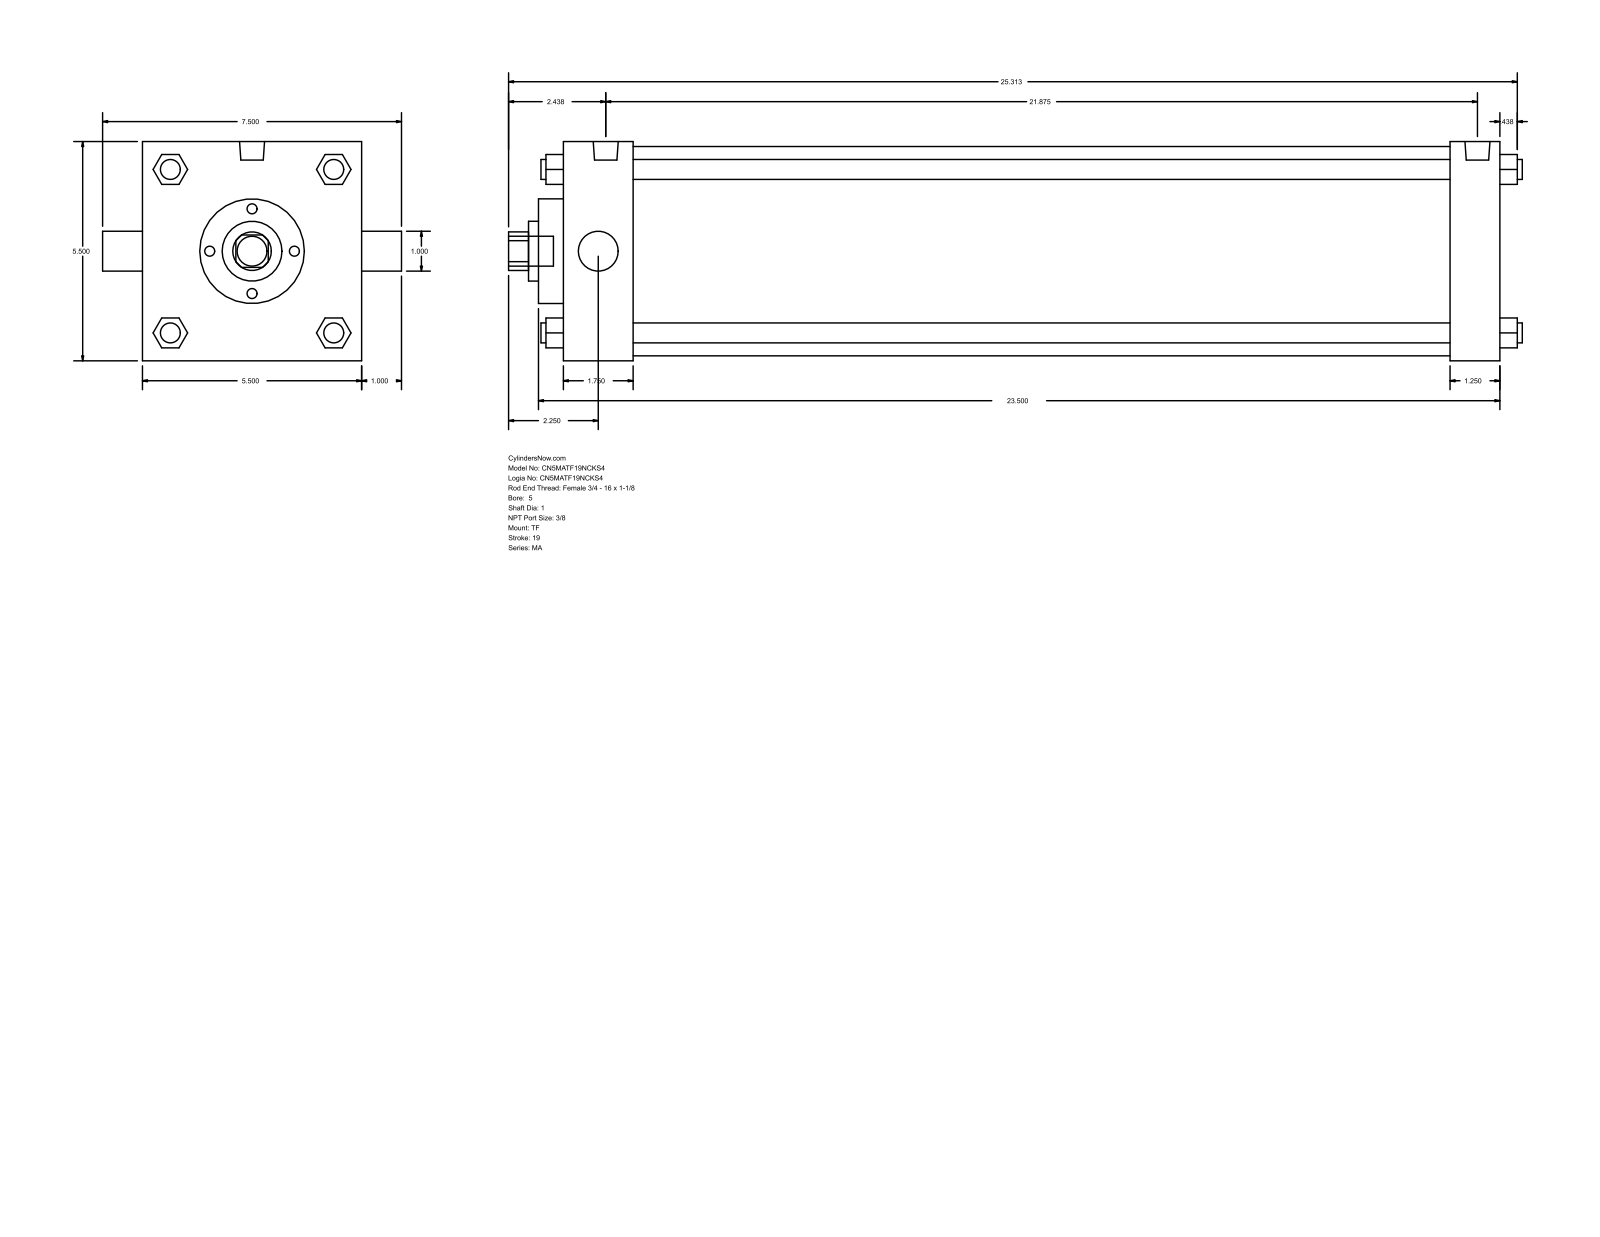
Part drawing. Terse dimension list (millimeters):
name: MA_TF__0500_1
written by: GSSL Pune (CONFIG_CONTROL_DESIGN)
unit: mm
bodies: 0 solids, 122 faces (93 planar, 29 cylindrical, 0 other)
size: 646.11 × 190.5 × 139.7
holes: 2× ⌀25.4, 1× ⌀38.1, 1× ⌀66.67, 1× ⌀133.35
bosses: 4× ⌀12.7, 3× ⌀11.11, 2× ⌀15.93, 1× ⌀19.05
rounds: 1× R12.29
face distances: 139.7, 596.91, 565.16, 31.75, 44.46, 520.7, 552.45, 15.87, 60.33, 581.03
